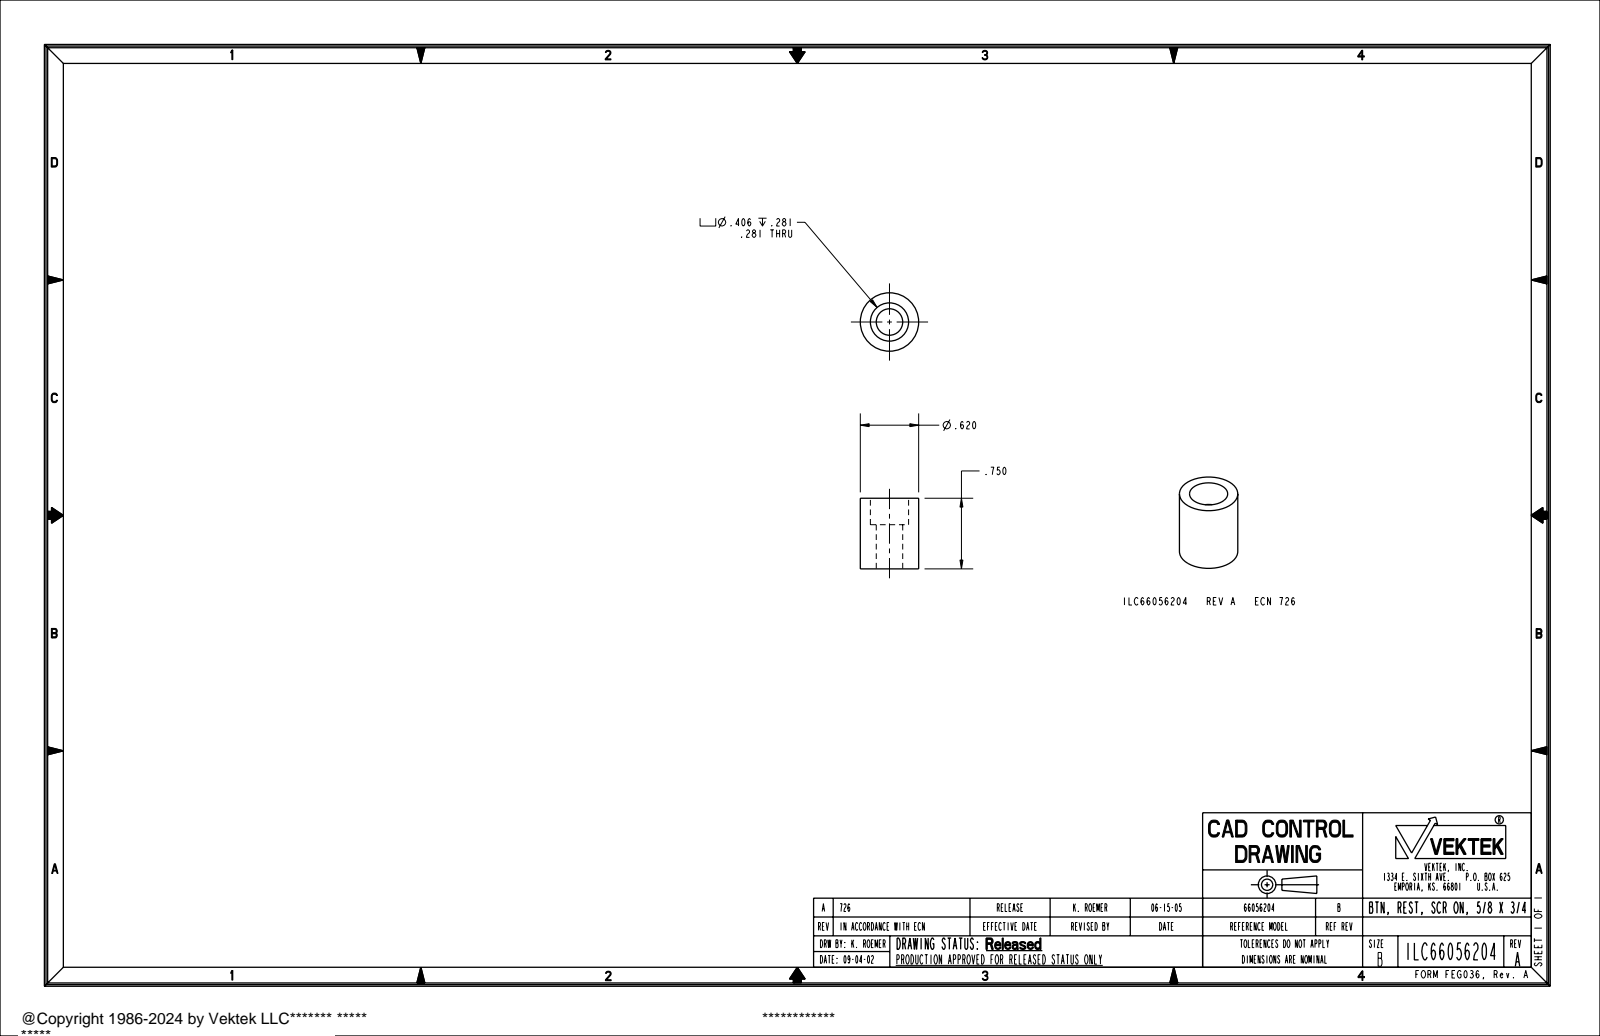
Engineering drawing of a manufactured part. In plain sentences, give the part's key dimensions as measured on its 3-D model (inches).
The part is named "ILC66056204". Its 3-D file was written by "PRO/ENGINEER BY PARAMETRIC TECHNOLOGY CORPORATION, 2004290 (AUTOMOTIVE_DESIGN_CC2)". It is 1 solid with 9 faces: 3 planar, 6 cylindrical and 0 other. Overall it measures 0.75 by 0.62 by 0.62 inches. Its volume is 0.161 cubic inches and its surface area 2.713 square inches. Round holes: 1 of diameter 0.281, 1 of diameter 0.406. Round bosses or shafts: 1 of diameter 0.62. The main face-to-face distances are 0.75, 0.469, 0.281.
